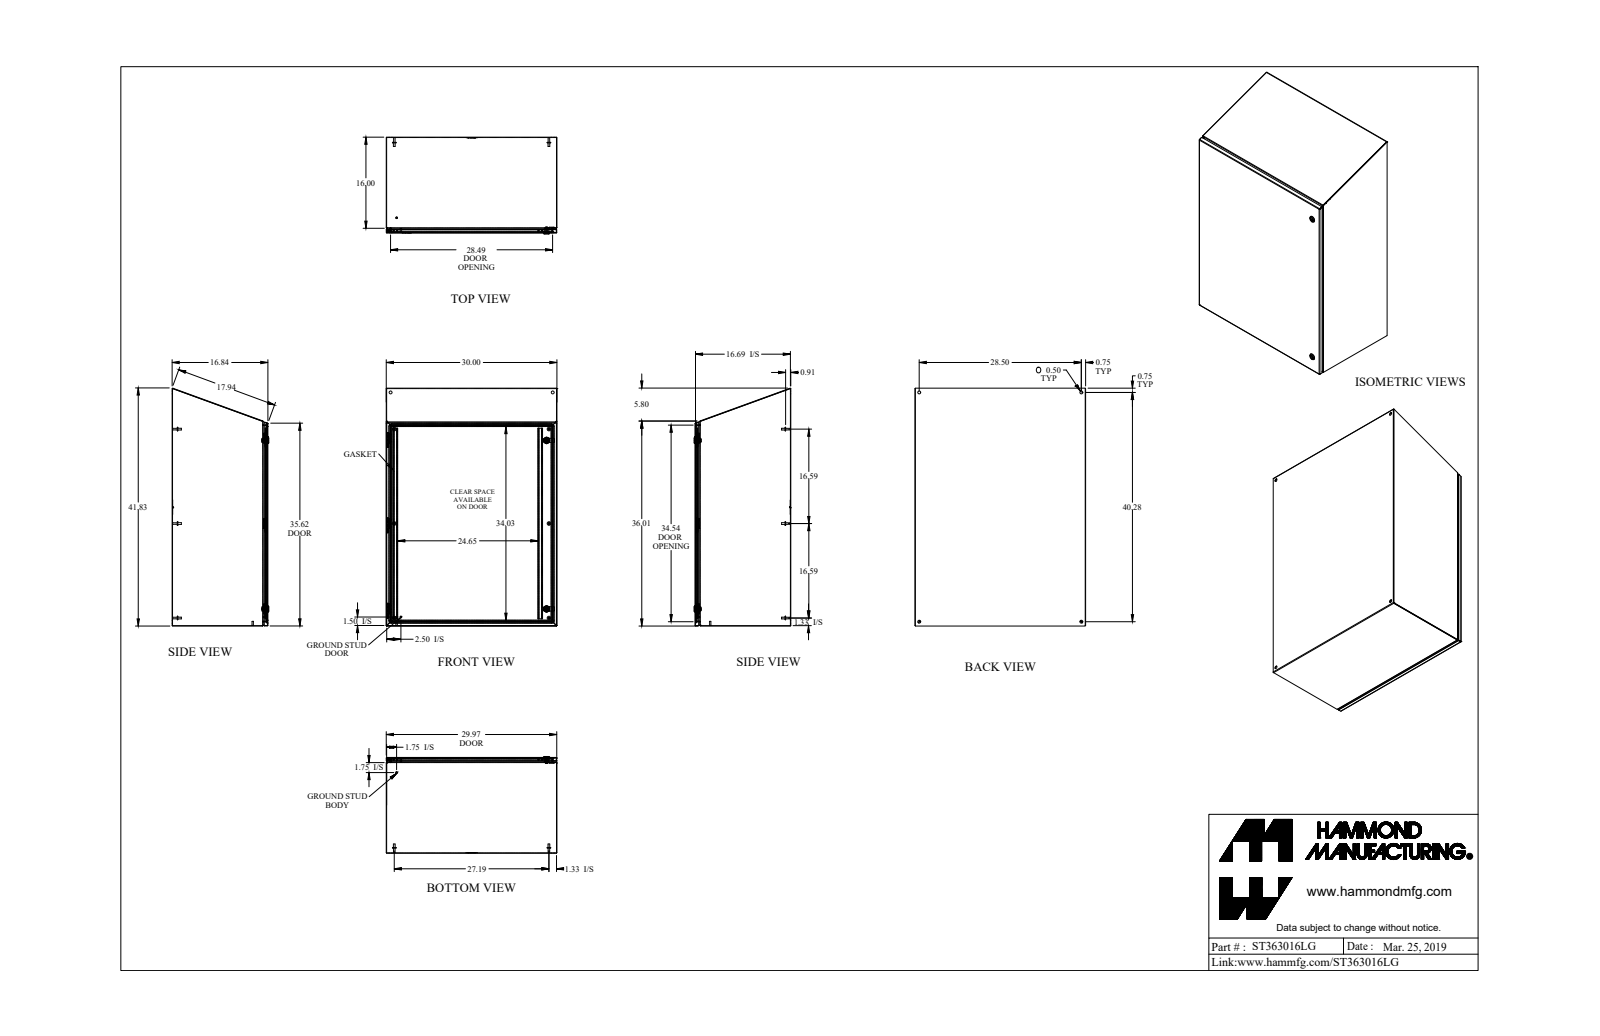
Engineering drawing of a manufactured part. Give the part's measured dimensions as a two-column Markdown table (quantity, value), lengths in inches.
| quantity | value |
| --- | --- |
| part name | ST363016LG |
| STEP written by | SolidWorks 2018 (AUTOMOTIVE_DESIGN) |
| units | inches |
| bodies | 35 solids, 900 faces (438 planar, 290 cylindrical, 172 other) |
| overall size | 41.784 × 30 × 16.997 |
| volume | 363.6 in³ |
| surface area | 10 186 in² |
| round holes (diameter × count) | 0.5 × 4, 0.172 × 2, 0.232 × 2, 0.24 × 2, 0.242 × 2, 0.625 × 2, 0.785 × 2 |
| round bosses / shafts (diameter × count) | 0.625 × 6, 0.313 × 6, 0.27 × 6, 1.1 × 2, 0.525 × 2, 0.455 × 2, 0.398 × 2, 0.356 × 2 |
| partial cylindrical surfaces (radius × count) | 0.036 × 18, 0.108 × 18, 0.043 × 12, 0.081 × 12, 0.006 × 6, 0.062 × 6, 0.188 × 5, 0.125 × 4 |
| main face-to-face distances | 0.072, 16.765, 29.928, 16.693, 16.837, 29.856, 30, 15.928, 0.837, 0.765 |
| hole center spacings | 28.5, 40.284, 49.346, 2.494, 8.496, 27.519, 28.693, 29.604 |
